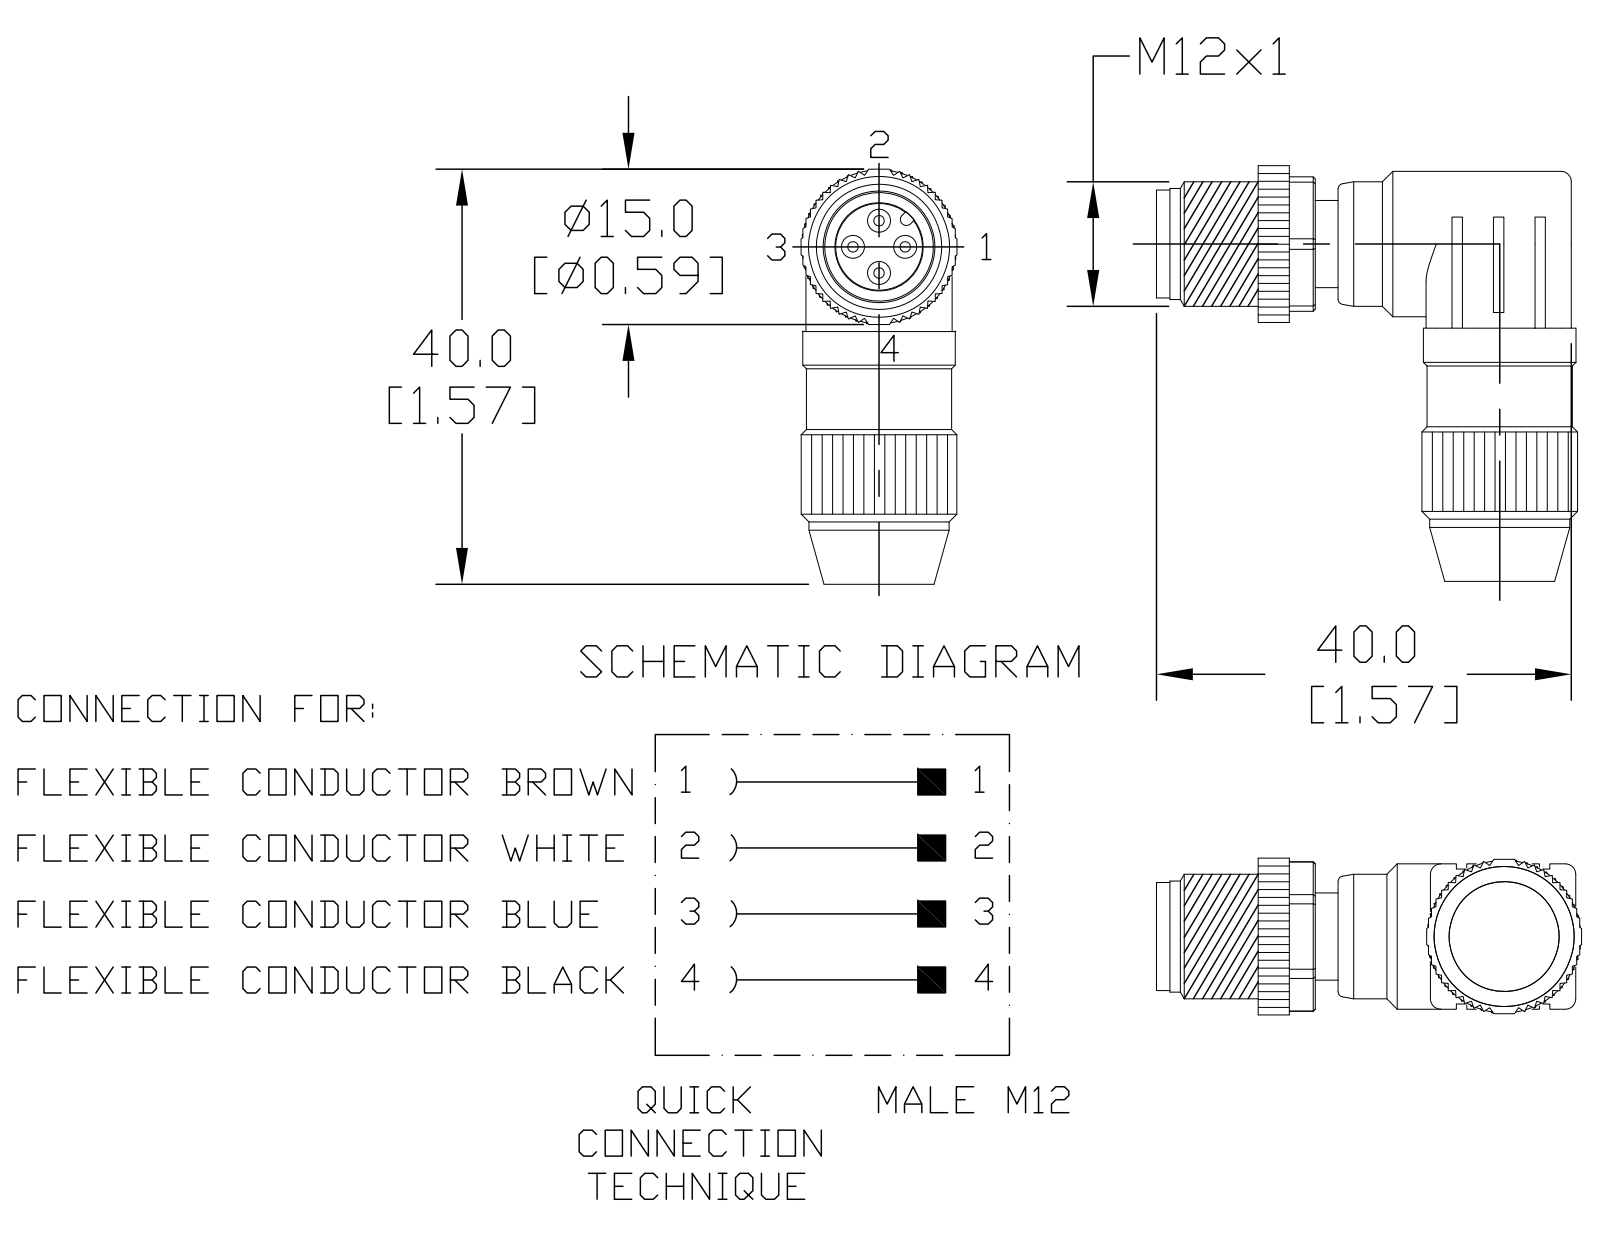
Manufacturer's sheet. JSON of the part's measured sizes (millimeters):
{"part_name": "7000-12561-0000000", "step_written_by": "SolidWorks 2015 (AUTOMOTIVE_DESIGN)", "units": "millimeters", "bodies": {"solids": 1, "faces": 489, "planar": 243, "cylindrical": 100, "other": 146}, "overall_size": [40, 40, 15], "volume_mm3": 9101, "surface_area_mm2": 4823, "round_holes": [[6.85, 1], [8.25, 1]], "round_bosses_or_shafts": [[1, 4], [15, 2], [13.84, 1], [13.74, 1], [13.34, 1], [12.9, 1], [10.54, 1], [9.13, 1]], "partial_cylinders_radius": [[0.5, 4], [5.84, 1]], "face_to_face_distances": [24.63, 30, 9.32, 15, 23.87, 6.13, 10.1, 9.82, 10, 0.76]}
